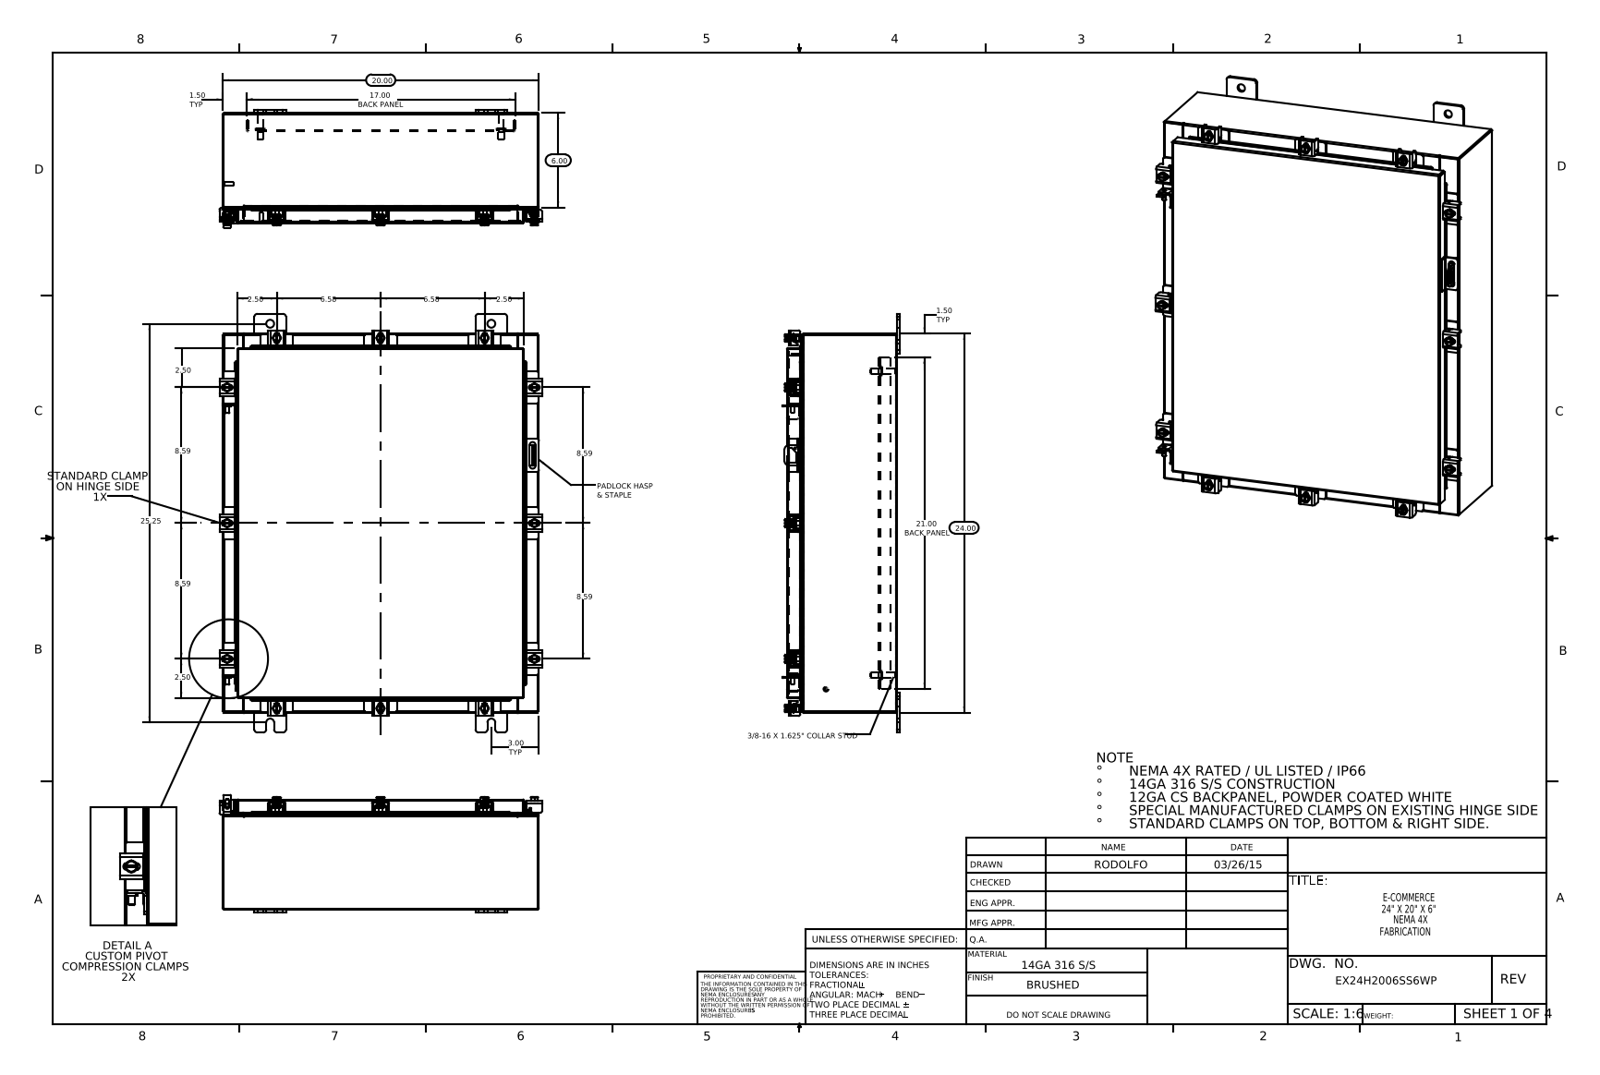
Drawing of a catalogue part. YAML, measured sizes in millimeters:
part_name: "EX24H2006SS6WP Standard Clamps; N-WMT04X30402202210-00 22104005_DEFAULT; EX24H2006SS6WP Cover; EX24H2006SS6WP Top (+8 more)"
step_written_by: "SolidWorks 2014 (CONFIG_CONTROL_DESIGN)"
units: millimeters
bodies: {solids: 81, faces: 2018, planar: 1075, cylindrical: 783, other: 160}
overall_size: [673.1, 518.7, 189.3]
volume: 2853000
surface_area: 2796000
round_holes:
  - {diameter: 5.4, count: 12}
  - {diameter: 6.6, count: 12}
  - {diameter: 12.7, count: 8}
  - {diameter: 3.2, count: 1}
  - {diameter: 6.4, count: 1}
round_bosses_or_shafts:
  - {diameter: 12.7, count: 12}
  - {diameter: 6.4, count: 12}
  - {diameter: 10.1, count: 10}
  - {diameter: 15.9, count: 4}
  - {diameter: 9.5, count: 4}
  - {diameter: 8.4, count: 4}
  - {diameter: 8, count: 2}
  - {diameter: 6, count: 2}
partial_cylinders:
  - {radius: 1.5, count: 54}
  - {radius: 0.3, count: 24}
  - {radius: 3.6, count: 24}
  - {radius: 4.8, count: 24}
  - {radius: 2.2, count: 22}
  - {radius: 3, count: 22}
  - {radius: 2.3, count: 18}
  - {radius: 1.3, count: 17}
face_to_face_distances: [1.9, 175.3, 177.2, 173.4, 2.6, 25.4, 27.3, 148, 149.9, 29.9]
hole_center_spacings: [59.6, 112.8, 218.3, 308.4, 421.7, 465.8, 510.1, 522.3]
